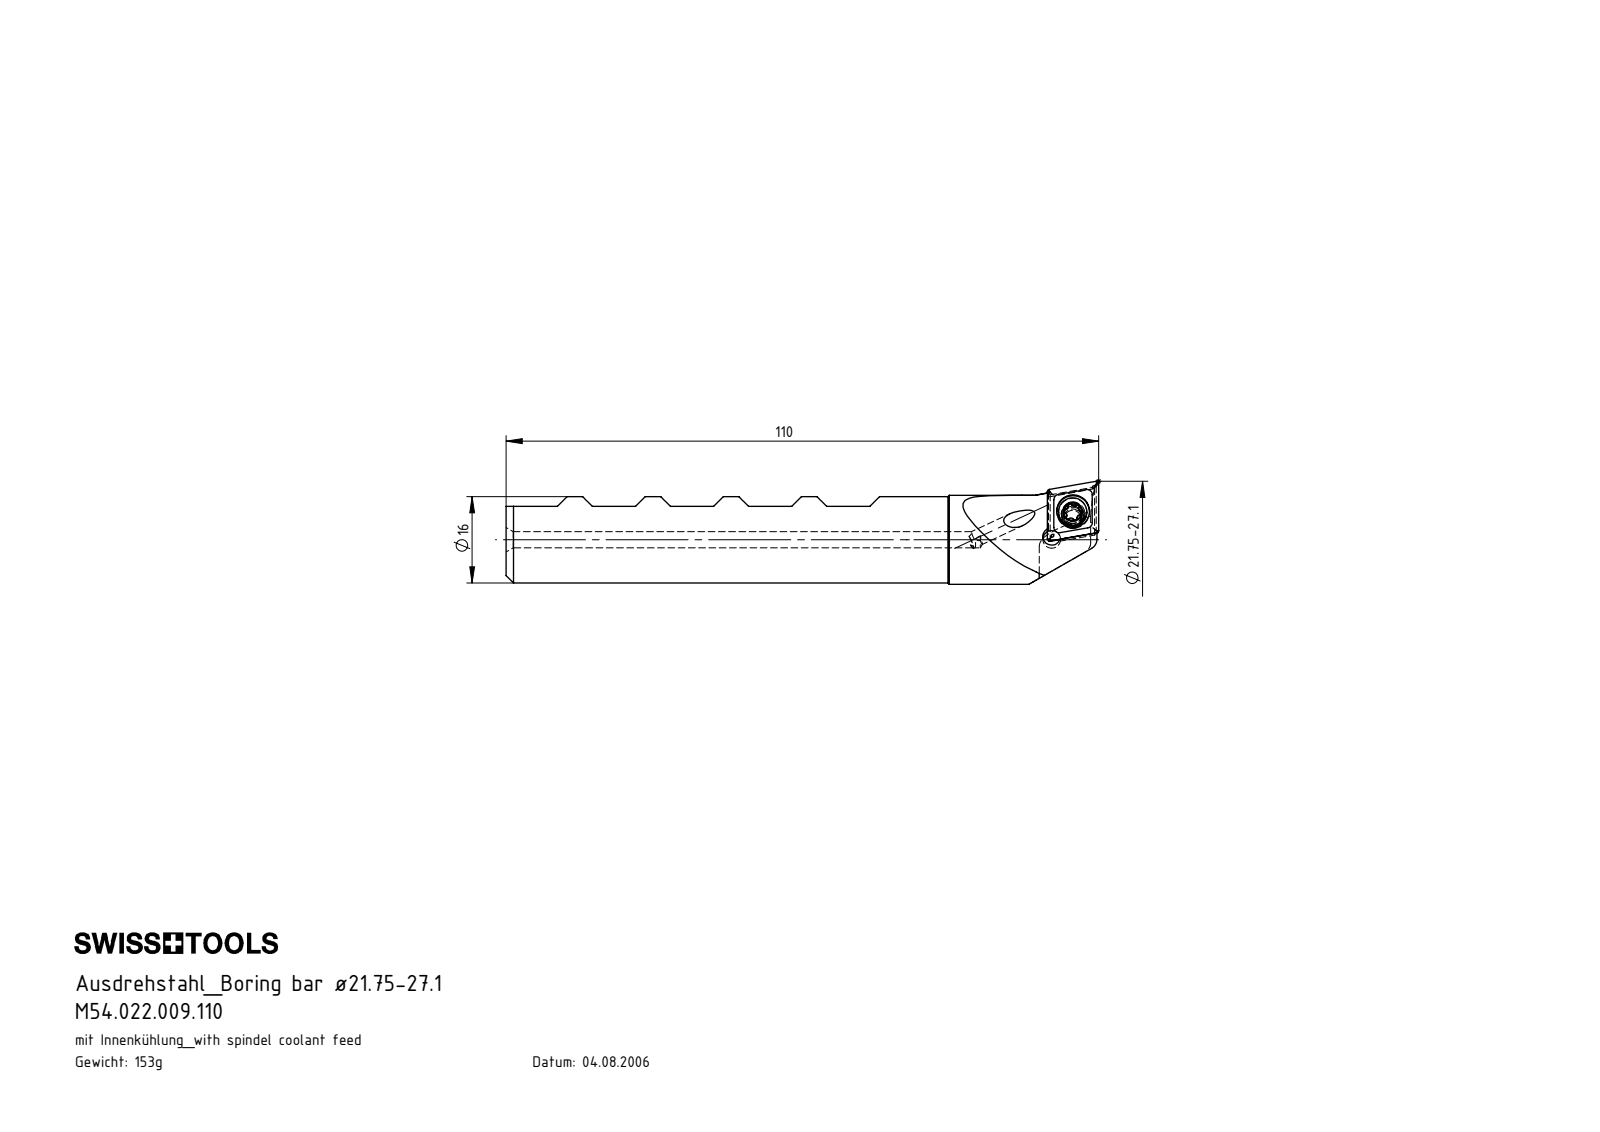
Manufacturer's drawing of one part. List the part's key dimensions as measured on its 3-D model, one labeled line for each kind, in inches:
Part name (STEP PRODUCT): B22.WCB.K11.110; CCMT09T304; WCB-ER2.001.009_A; B22-WCB.K11.110_B
STEP written by: SolidWorks 2017 (AUTOMOTIVE_DESIGN)
Units: inches
Bodies: 3 solids, 118 faces (45 planar, 27 cylindrical, 46 other)
Overall size (bounding box): 4.331 × 0.753 × 0.683
Volume: 1.187 in³ · Surface area: 11.06 in²
Round holes (diameter × count): ⌀0.118 ×2, ⌀0.13 ×2, ⌀0.173 ×1, ⌀0.24 ×1
Round bosses / shafts (diameter × count): ⌀0.65 ×1, ⌀0.63 ×1, ⌀0.207 ×1, ⌀0.157 ×1
Partial cylindrical surfaces — rounded edges, fillets, slot ends (radius × count): R0.013 ×6, R0.023 ×6, R0.079 ×1, R0.331 ×1, R0.472 ×1
Main face-to-face distances: 0.404, 0.807, 1.211, 0.807, 0.234, 0.382, 0.148, 0.39, 0.156, 1.211
Hole centre spacings: 0.239, 0.244
